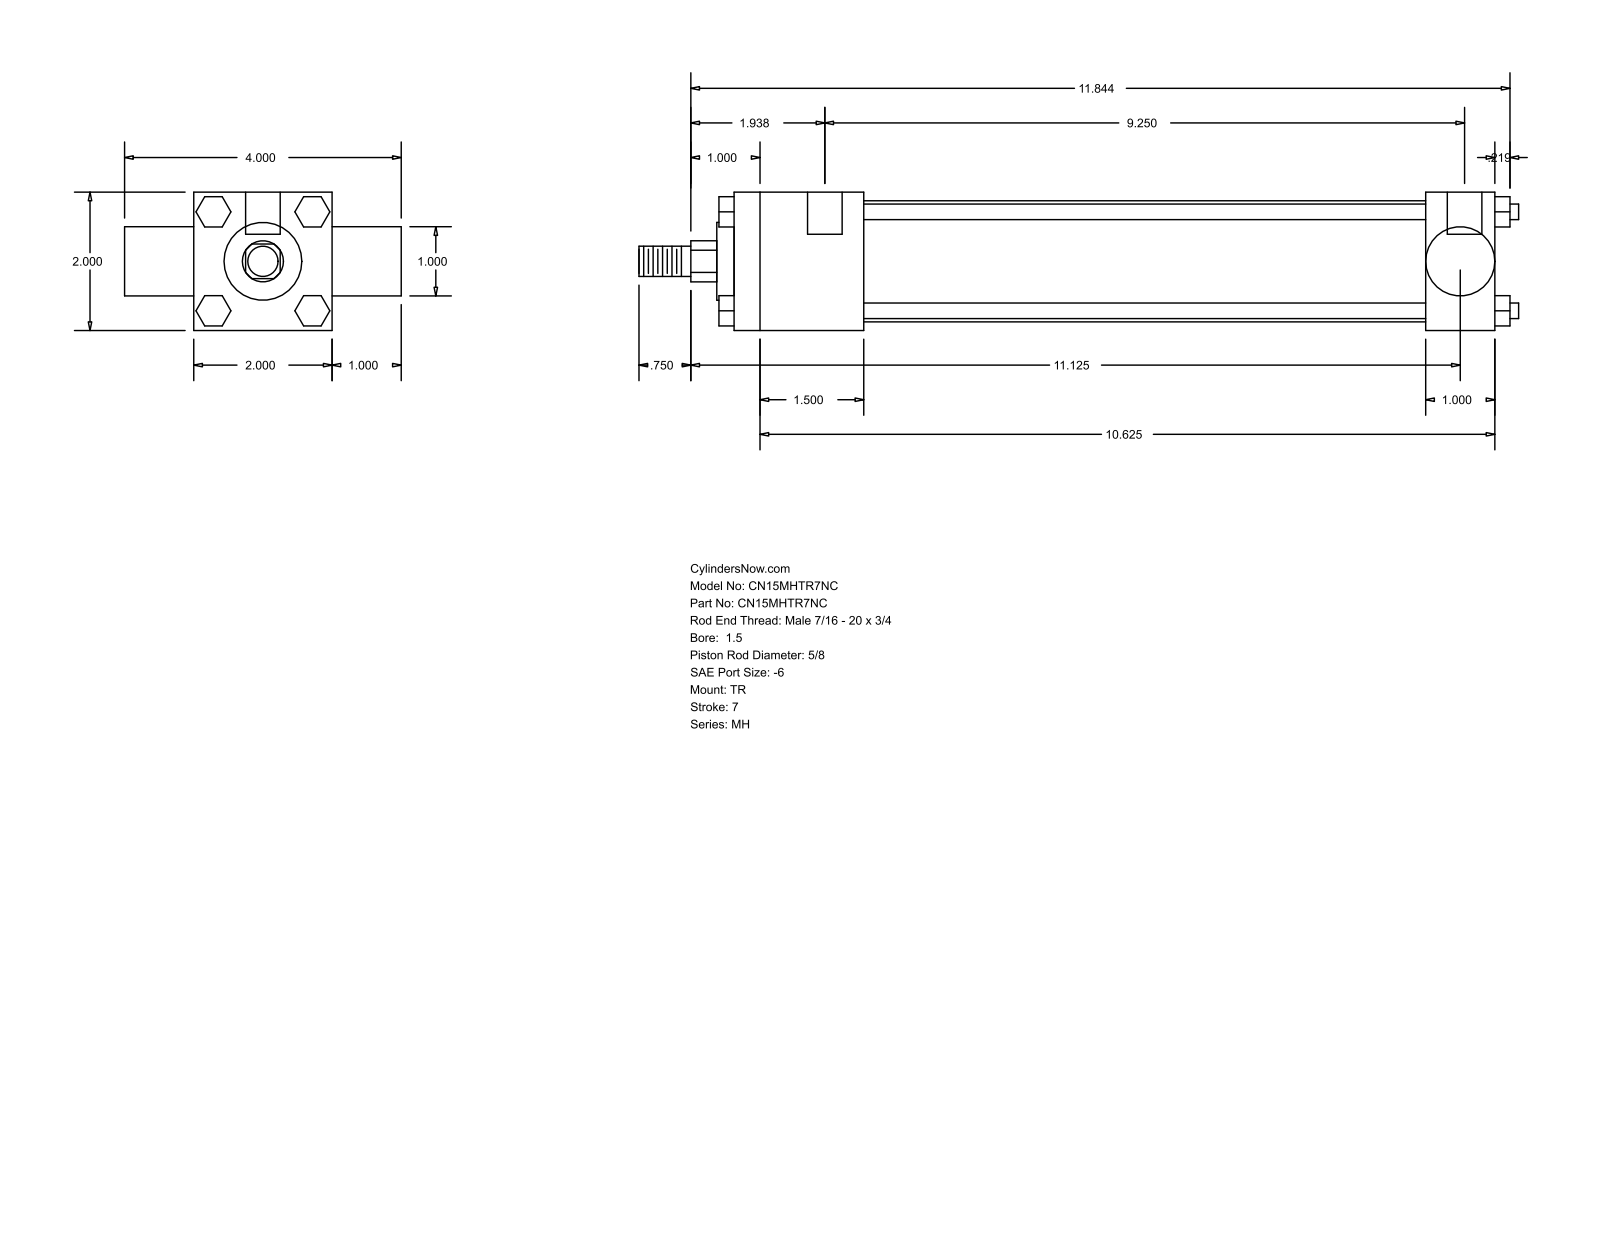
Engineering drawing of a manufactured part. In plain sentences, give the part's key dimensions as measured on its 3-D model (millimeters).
The part is named "MH_TR__0150_0.625". Its 3-D file was written by "GSSL Pune (CONFIG_CONTROL_DESIGN)". It is 0 solids with 120 faces: 92 planar, 28 cylindrical and 0 other. Overall it measures 323.06 by 101.6 by 50.8 millimeters. Round holes: 3 of diameter 5.56, 2 of diameter 12.7. Round bosses or shafts: 4 of diameter 5.71, 1 of diameter 44.45, 1 of diameter 28.57, 1 of diameter 25.35, 1 of diameter 15.88, 1 of diameter 11.11. Partial cylindrical surfaces (rounded edges, fillets, slot ends): 1 of radius 7.54. The main face-to-face distances are 50.8, 279.39, 25.4, 76.2, 47.62, 231.77, 254, 206.38, 25.39, 5.56. The hole center spacings are 3.17, 234.95, 238.12.
